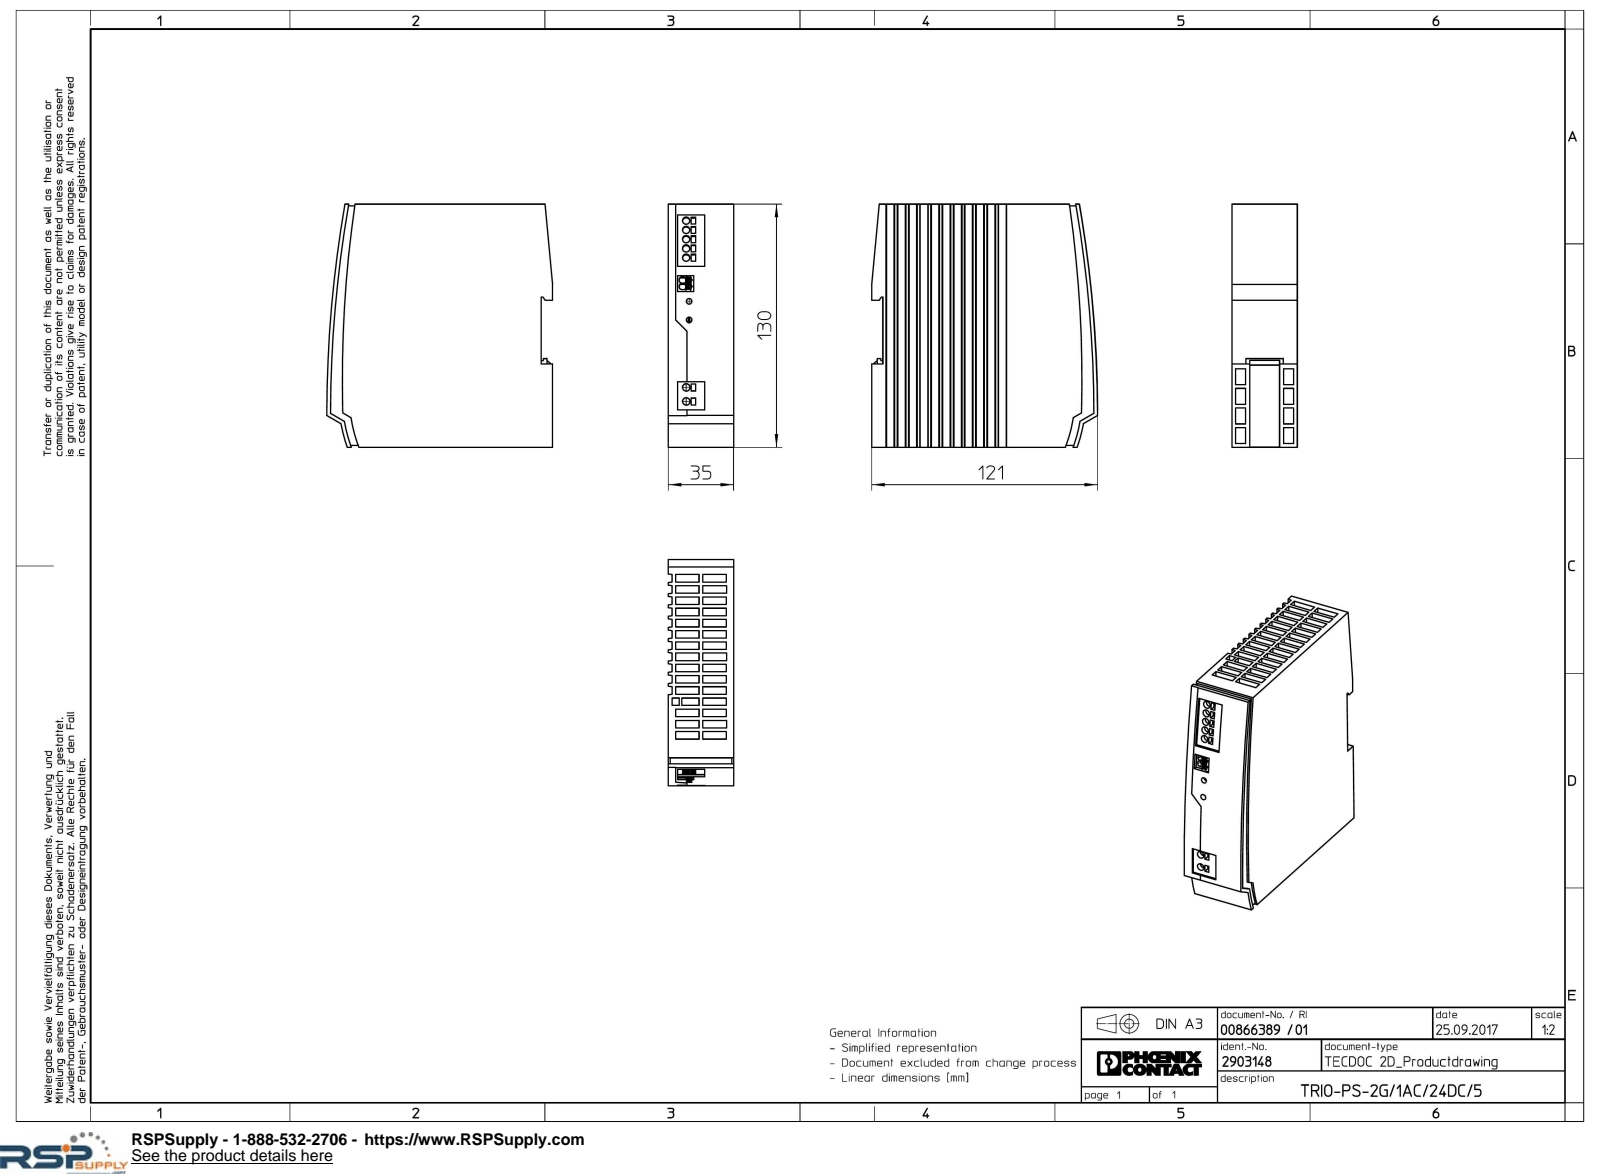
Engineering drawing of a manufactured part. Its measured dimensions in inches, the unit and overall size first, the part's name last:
Units: inches
Overall size (bounding box): 5.118 × 4.764 × 1.378
Round holes (diameter × count): ⌀0.157 ×7, ⌀0.118 ×2
Partial cylindrical surfaces — rounded edges, fillets, slot ends (radius × count): R0.022 ×2, R0.024 ×2, R0.041 ×2, R0.041 ×2, R2.722 ×1, R2.874 ×1, R2.953 ×1, R25.812 ×1
Main face-to-face distances: 1.378, 0.079, 1.299, 0.118, 0.467, 0.701, 0.233, 1.168, 5, 0.039
Hole centre spacings: 0.197, 0.394, 0.295, 0.59, 0.591, 0.787
Volume: 30.38 in³ · Surface area: 93.39 in²
Bodies: 1 solid, 610 faces (573 planar, 33 cylindrical, 4 other)
Part name (STEP PRODUCT): TRIO_PS_2G_1AC_24DC_5-select
STEP written by: Creo Elements/Direct Modeling 18.1I 14-Aug-2016 (C) Parametric Technology GmbH (AUTOMOTIVE_DESIGN)
